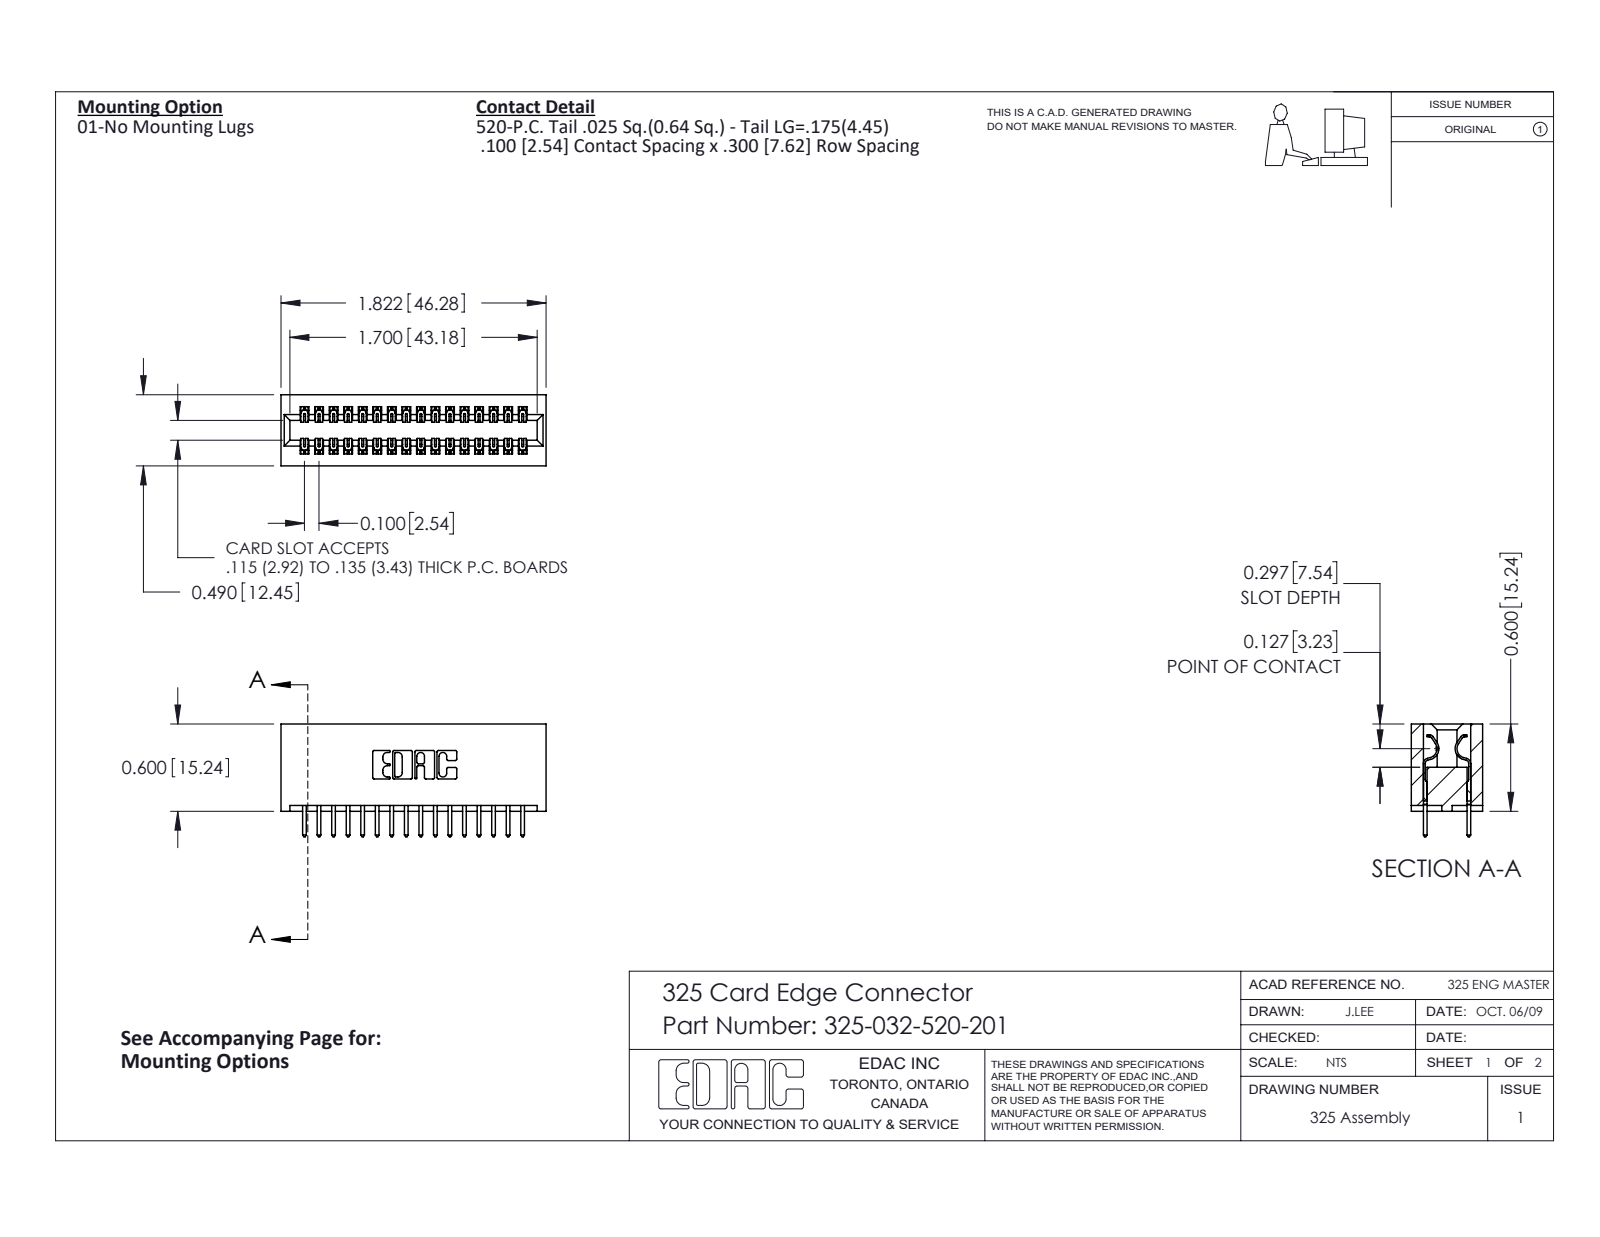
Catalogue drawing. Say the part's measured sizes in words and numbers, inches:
The part is named "325 Part_Lugless; 325-032-520-201; 325-292-001_325-293-120". Its 3-D file was written by "SolidWorks 2016 (CONFIG_CONTROL_DESIGN)". It is 33 solids with 1770 faces: 1218 planar, 552 cylindrical and 0 other. Overall it measures 1.822 by 0.775 by 0.49 inches. Its volume is 0.387 cubic inches and its surface area 11.87 square inches. Partial cylindrical surfaces (rounded edges, fillets, slot ends): 48 of radius 0.006, 32 of radius 0.01, 22 of radius 0.01, 6 of radius 0.007, 6 of radius 0.031, 3 of radius 0.026, 2 of radius 0.014, 2 of radius 0.022. The main face-to-face distances are 0.083, 0.407, 0.3, 0.49, 0.107, 0.383, 0.025, 0.325, 0.1, 0.2.
